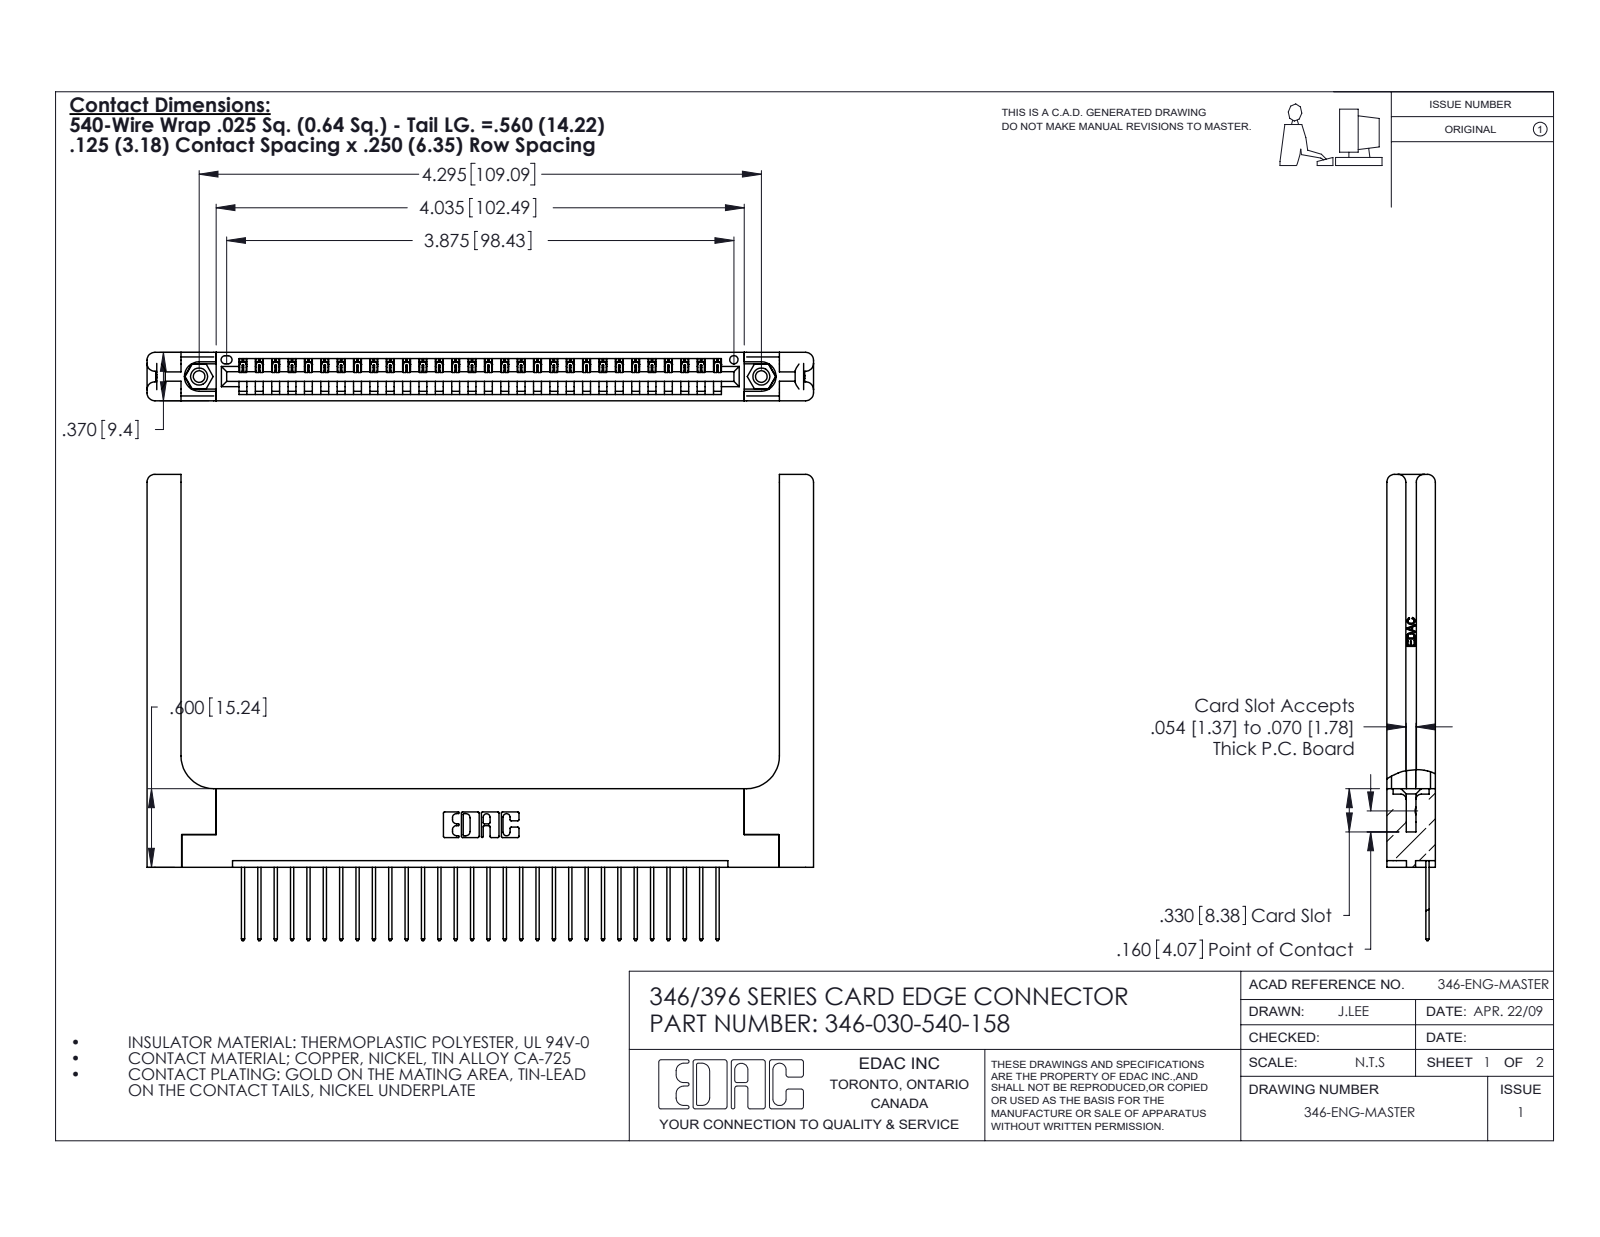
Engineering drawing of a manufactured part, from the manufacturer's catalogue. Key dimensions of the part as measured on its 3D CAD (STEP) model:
Part name (STEP PRODUCT): 346 Part_Flush Mounting Lugs - 0.156 Dia-TH; 345-292-001_345-293-140; 346-220-058_345-220-058; 345-250-001_345-250-001-102 (+1 more)
STEP written by: SolidWorks 2020 (CONFIG_CONTROL_DESIGN)
Units: inches
Bodies: 35 solids, 2132 faces (1438 planar, 634 cylindrical, 60 other)
Overall size (bounding box): 5.091 × 3.56 × 0.37
Volume: 1.21 in³ · Surface area: 32.19 in²
Round holes (diameter × count): ⌀0.089 ×2, ⌀0.125 ×2, ⌀0.156 ×2, ⌀0.064 ×1
Round bosses / shafts (diameter × count): ⌀0.155 ×2
Partial cylindrical surfaces — rounded edges, fillets, slot ends (radius × count): R0.006 ×60, R0.01 ×60, R0.01 ×22, R0.06 ×16, R0.007 ×6, R0.031 ×6, R0.026 ×3, R0.03 ×2
Main face-to-face distances: 0.37, 0.072, 0.048, 0.322, 0.148, 0.15, 0.25, 0.298, 0.025, 0.076
Hole centre spacings: 0.246, 4.087, 4.295
